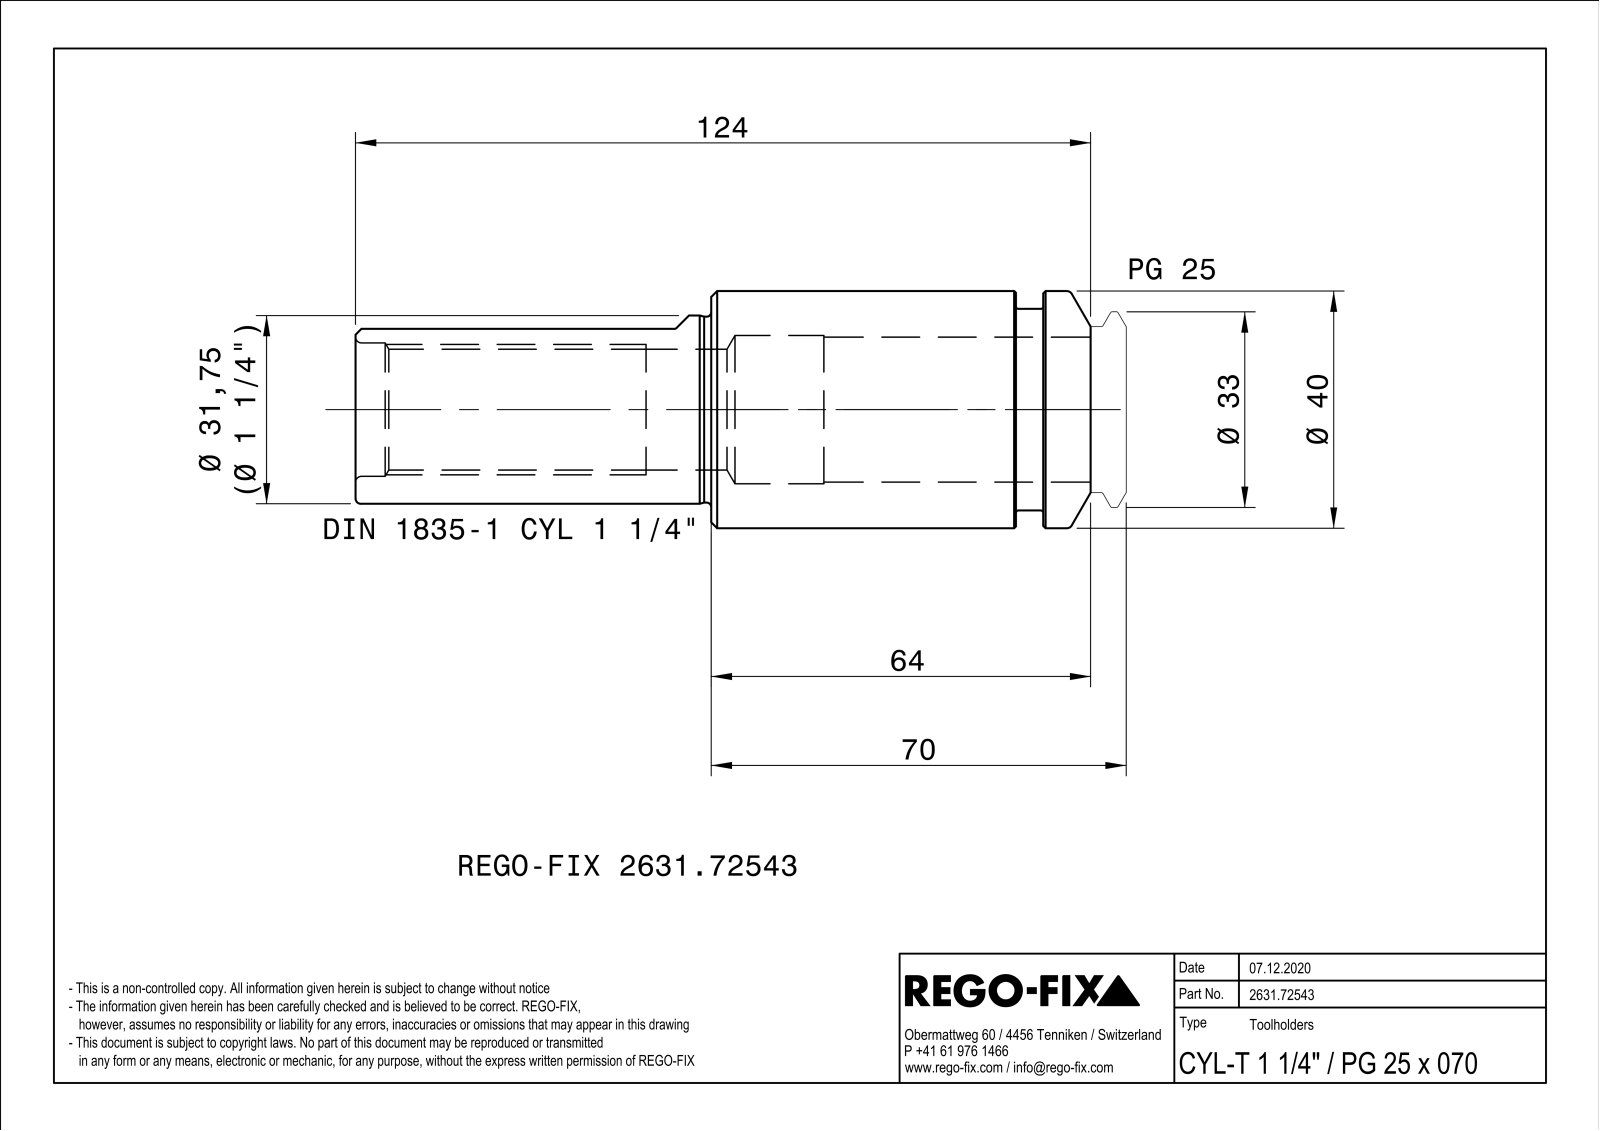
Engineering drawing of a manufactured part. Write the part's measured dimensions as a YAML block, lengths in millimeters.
part_name: "NOCUT"
step_written_by: "SIEMENS PLM Software Solid Edge ST10 (AUTOMOTIVE_DESIGN)"
units: millimeters
bodies: {solids: 1, faces: 38, planar: 9, cylindrical: 11, other: 18}
overall_size: [124, 40, 40]
volume: 73328
surface_area: 24541
round_holes:
  - {diameter: 20.38, count: 1}
  - {diameter: 22.5, count: 1}
  - {diameter: 25, count: 1}
round_bosses_or_shafts:
  - {diameter: 40, count: 1}
  - {diameter: 34, count: 1}
  - {diameter: 31.75, count: 1}
  - {diameter: 31.35, count: 1}
partial_cylinders:
  - {radius: 0.5, count: 1}
face_to_face_distances: [51.4, 4.6, 56, 116, 111.4, 60, 8, 12.6, 64, 124]
